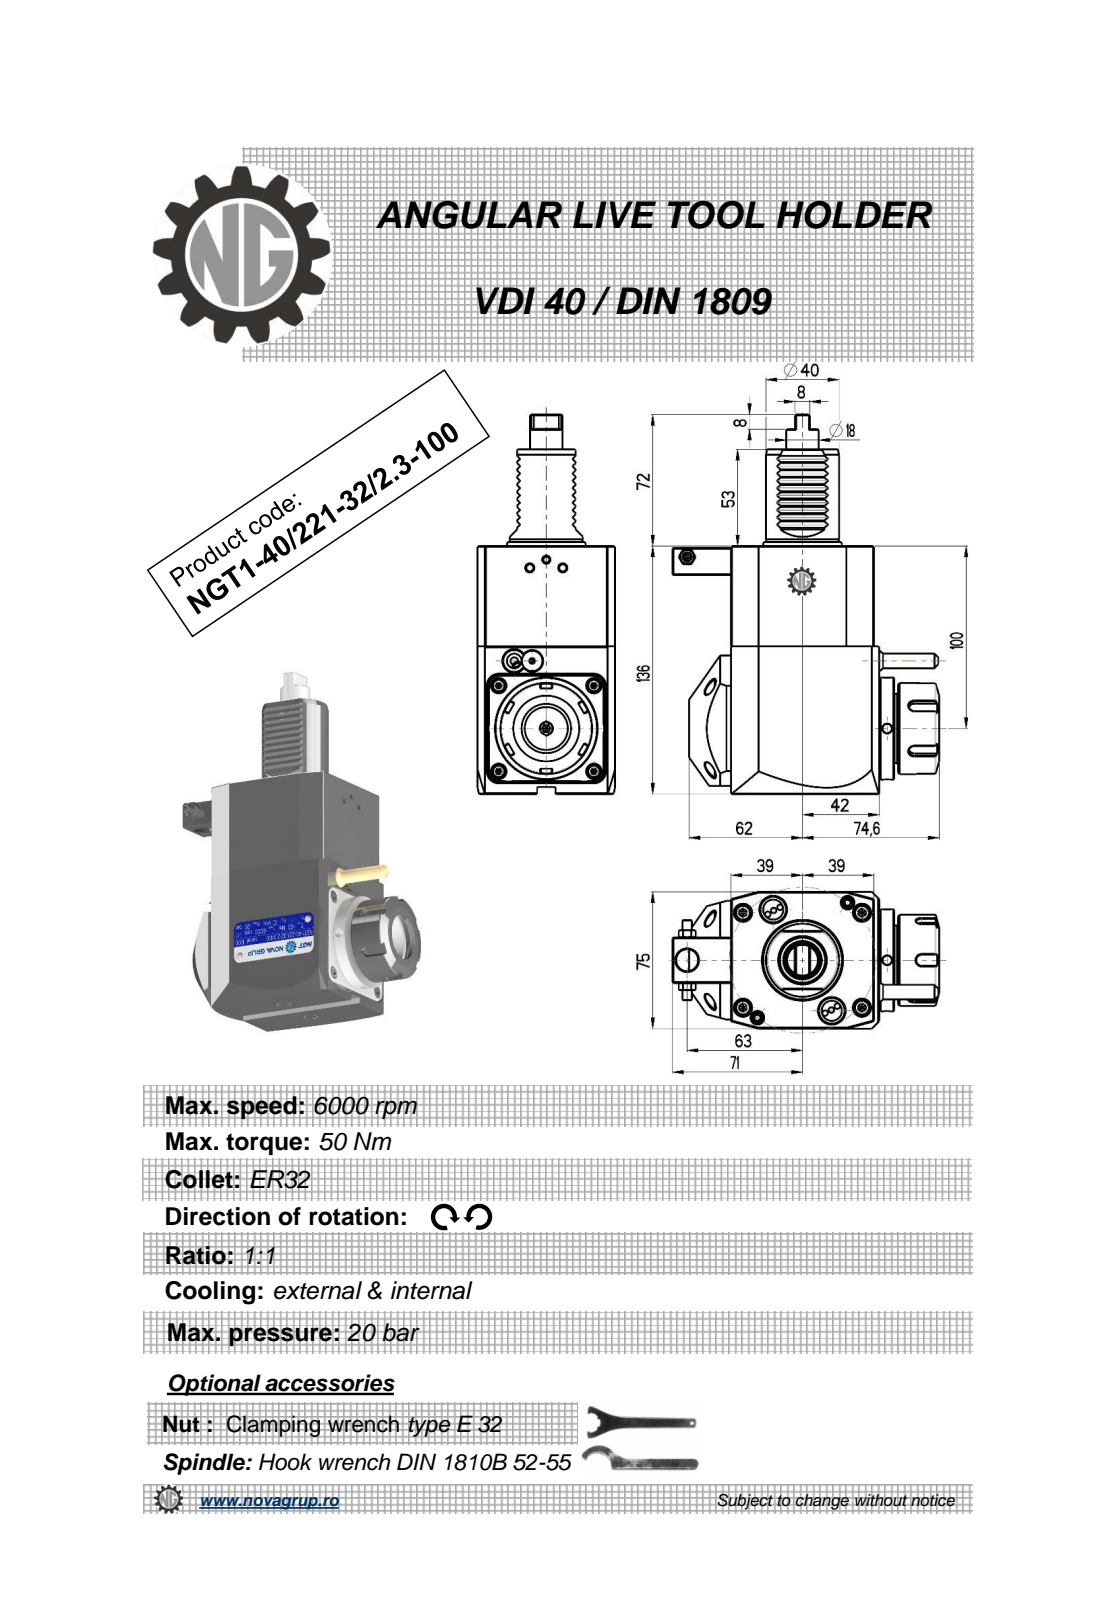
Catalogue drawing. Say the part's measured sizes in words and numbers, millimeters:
The part is named "NGT1_40_221_32_2_3_100". Its 3-D file was written by "PRO/ENGINEER BY PARAMETRIC TECHNOLOGY CORPORATION, 2010280 (CONFIG_CONTROL_DESIGN)". It is 1 solid with 455 faces: 224 planar, 94 cylindrical and 137 other. Overall it measures 208 by 145.6 by 75 millimeters. Its volume is 998 000 cubic millimeters and its surface area 77 423 square millimeters. Round holes: 3 of diameter 5, 1 of diameter 3, 1 of diameter 4.2, 1 of diameter 9.5, 1 of diameter 12, 1 of diameter 27. Round bosses or shafts: 1 of diameter 56, 1 of diameter 50, 1 of diameter 43, 1 of diameter 40, 1 of diameter 17.8, 1 of diameter 11.2, 1 of diameter 8.96, 1 of diameter 8. Partial cylindrical surfaces (rounded edges, fillets, slot ends): 20 of radius 0.3, 12 of radius 0.26, 6 of radius 0.22, 5 of radius 3, 2 of radius 0.8, 1 of radius 40. The main face-to-face distances are 75, 136, 78, 81, 3, 84.88, 80.8, 2.8, 7.5, 11. The hole center spacings are 40.93, 58.19, 92.5, 109.25, 144.12.
